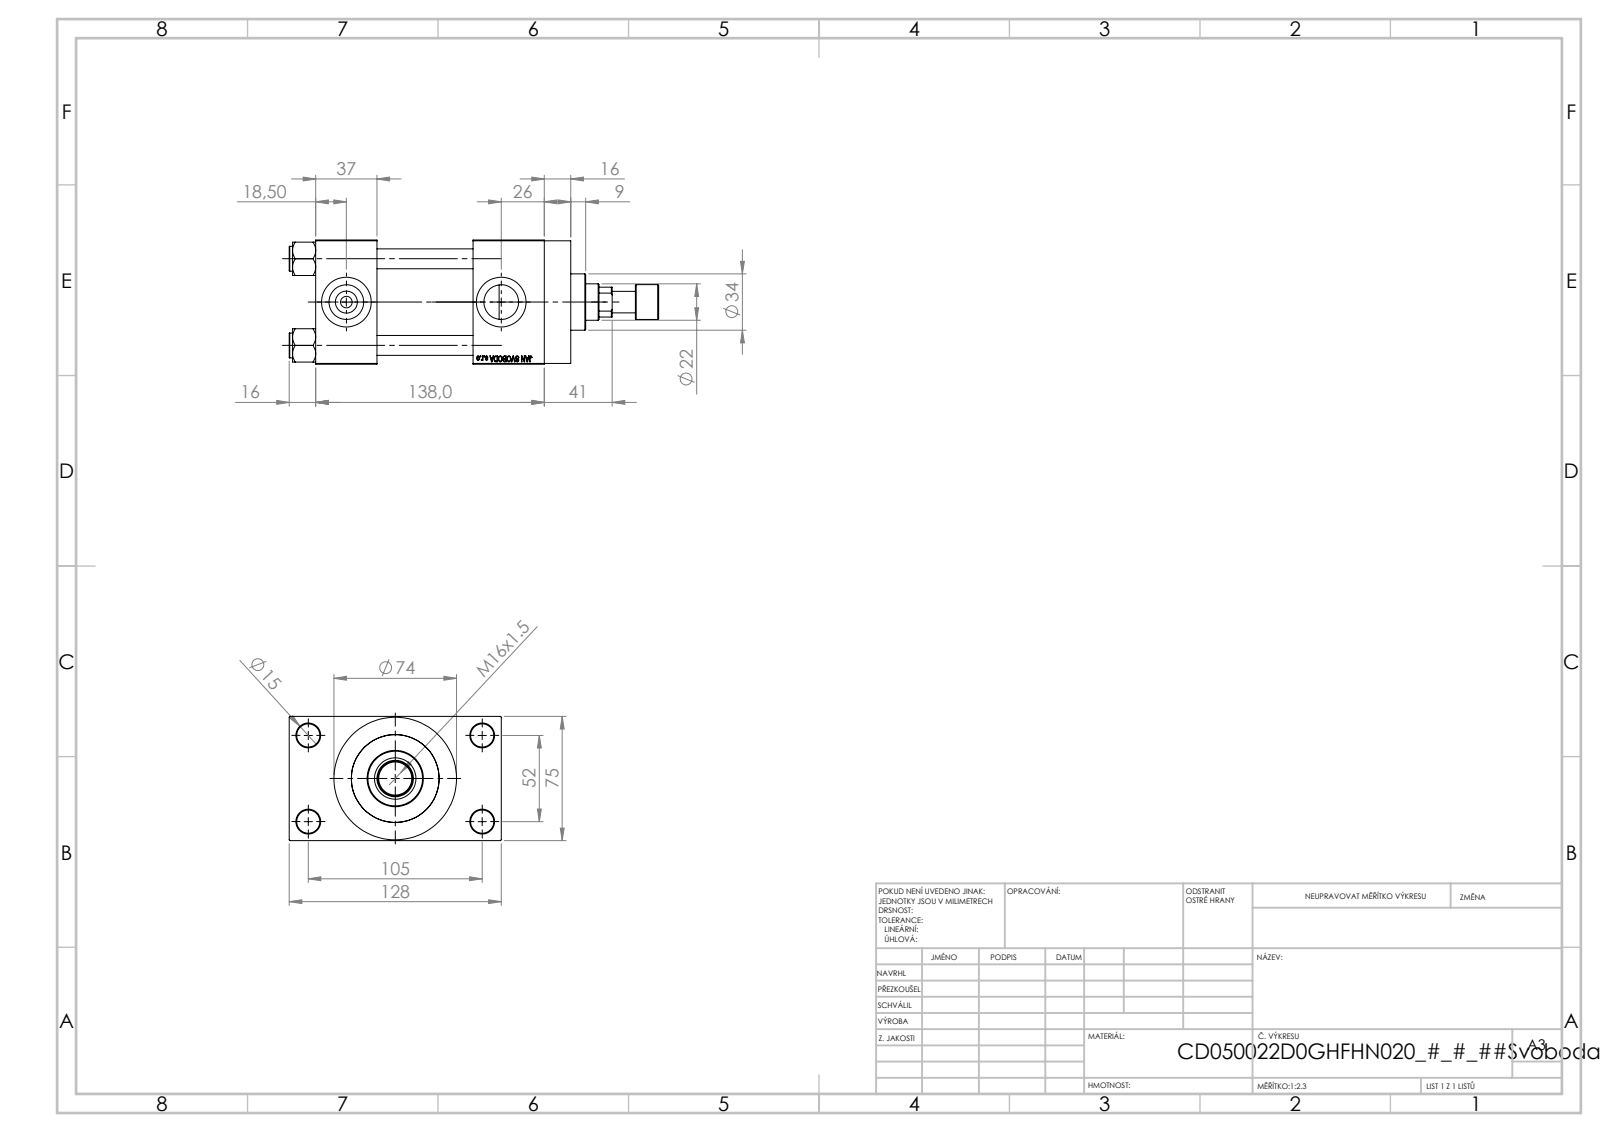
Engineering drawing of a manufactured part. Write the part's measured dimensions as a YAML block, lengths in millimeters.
part_name: "V215CD_VC_A; V215CD_VCP_D; V215CD_NUT_M5_D; V215CR_ROD_END_F (+2 more)"
step_written_by: "SolidWorks 2019 (CONFIG_CONTROL_DESIGN)"
units: millimeters
bodies: {solids: 12, faces: 1114, planar: 500, cylindrical: 92, other: 522}
overall_size: [223, 128, 75]
volume: 804218
surface_area: 168846
round_holes:
  - {diameter: 12, count: 4}
  - {diameter: 14, count: 4}
  - {diameter: 7, count: 2}
  - {diameter: 20.96, count: 2}
  - {diameter: 30, count: 2}
  - {diameter: 10.5, count: 1}
  - {diameter: 22, count: 1}
  - {diameter: 25, count: 1}
  - {diameter: 41, count: 1}
  - {diameter: 50, count: 1}
  - {diameter: 53, count: 1}
round_bosses_or_shafts:
  - {diameter: 15, count: 4}
  - {diameter: 74, count: 1}
  - {diameter: 56, count: 1}
  - {diameter: 34, count: 1}
  - {diameter: 21, count: 1}
  - {diameter: 13, count: 1}
face_to_face_distances: [75, 58, 37, 95, 26.5, 138, 101, 43, 101.5, 16]
hole_center_spacings: [26.35, 36.98, 52.3, 58.43, 58.59, 78.65, 94.37, 52]
